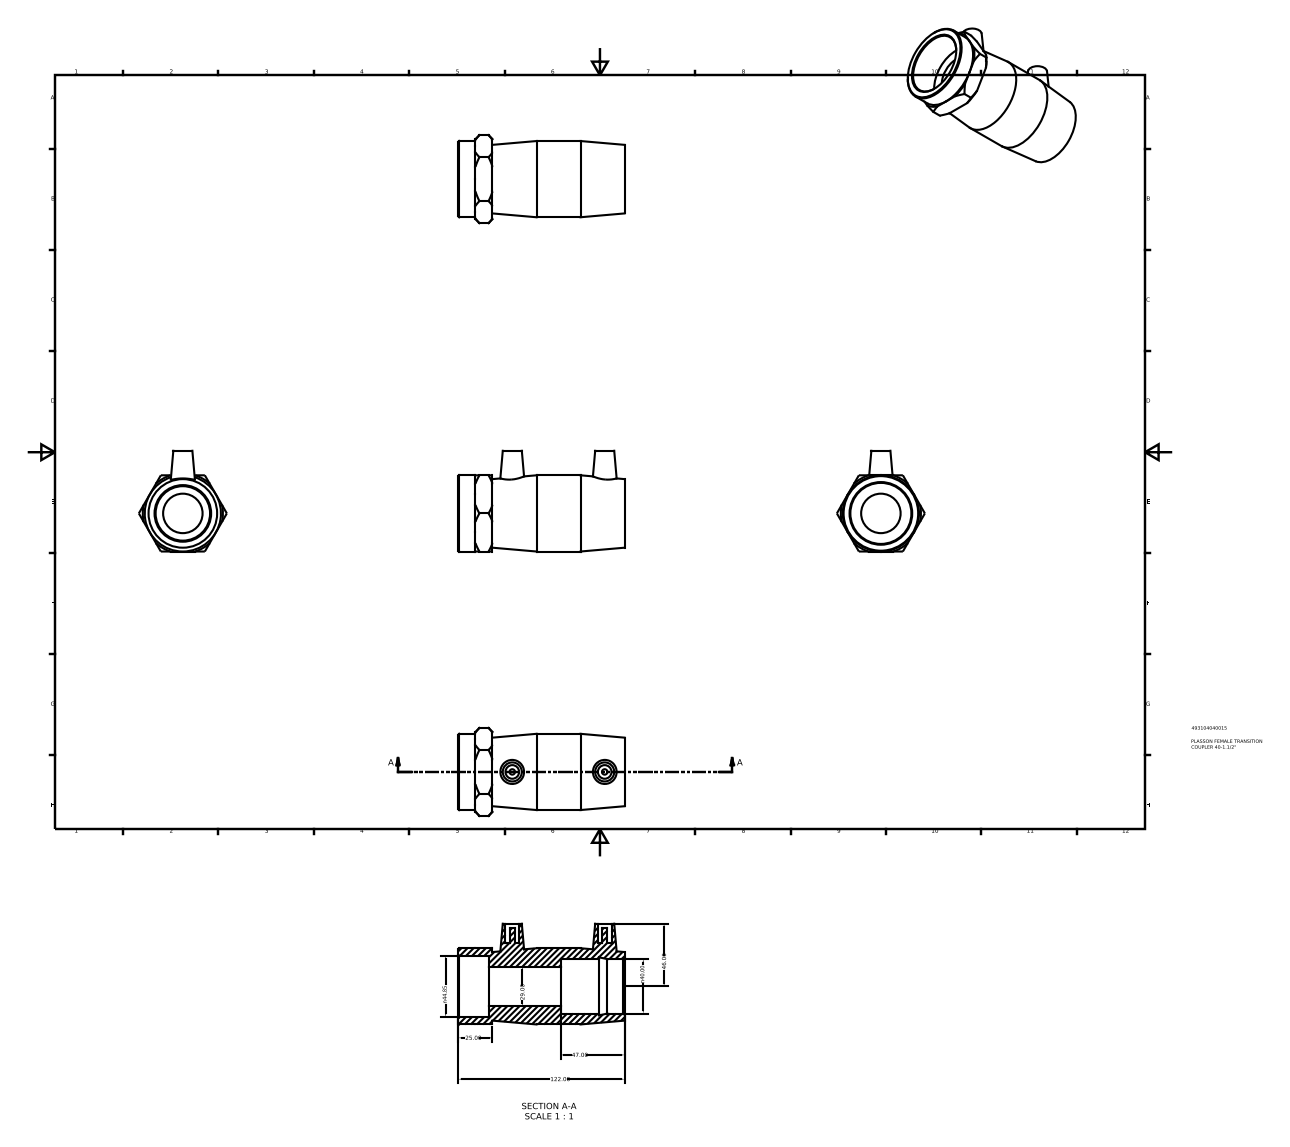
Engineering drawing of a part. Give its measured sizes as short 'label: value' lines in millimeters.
name: 493104040015
written by: Autodesk Inventor 2015 (AUTOMOTIVE_DESIGN)
unit: mm
bodies: 1 solid, 54 faces (24 planar, 10 cylindrical, 20 other)
size: 122 × 74 × 64.66
volume: 164 017 mm³; area: 42 024 mm²
holes: 2× ⌀10, 1× ⌀29, 1× ⌀40, 1× ⌀44.84
bosses: 2× ⌀4, 1× ⌀56
face distances: 56, 22.5, 122, 99.5, 25, 2.5, 97, 75, 52.5, 50
hole spacings: 67.9
